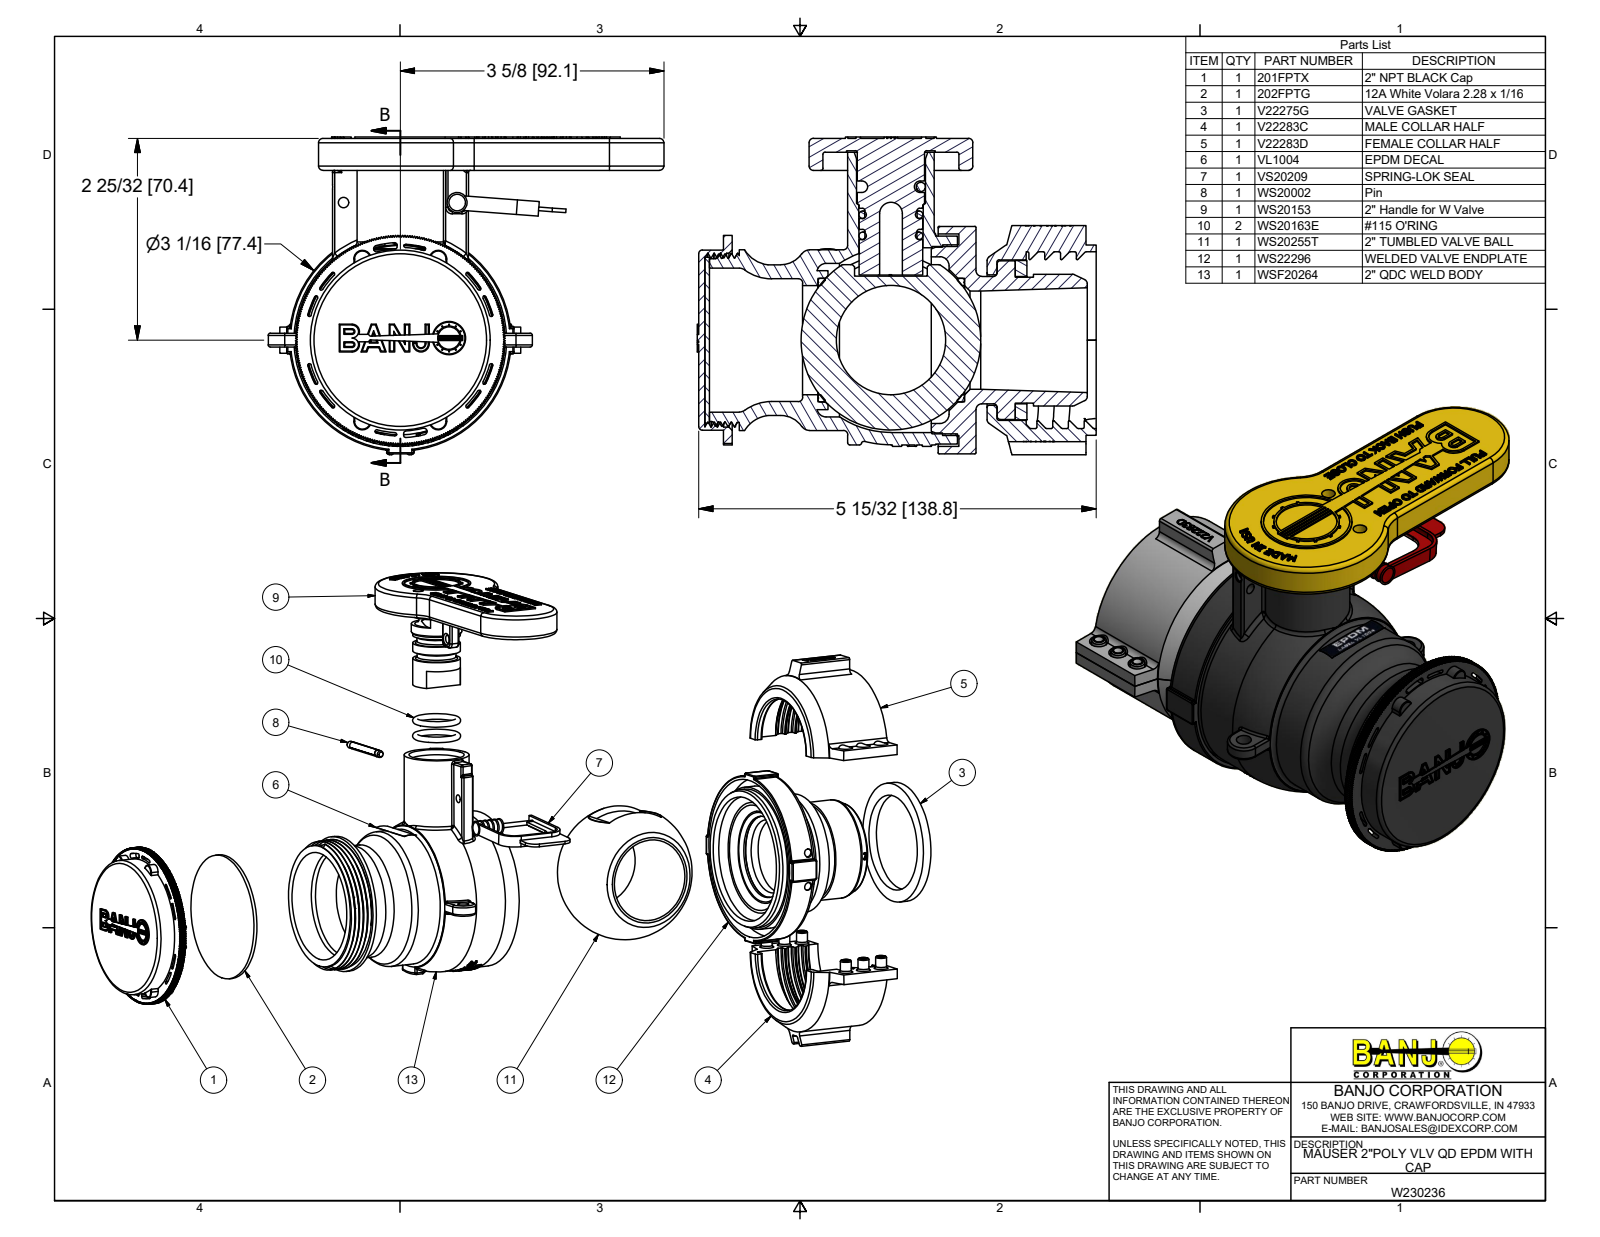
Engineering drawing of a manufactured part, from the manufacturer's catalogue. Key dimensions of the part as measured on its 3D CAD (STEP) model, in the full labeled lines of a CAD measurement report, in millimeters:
Part name (STEP PRODUCT): W230236; VS20209; 201FPTX; 202FPTG (+8 more)
STEP written by: Autodesk Inventor 2018 (AUTOMOTIVE_DESIGN)
Units: millimetres
Bodies: 16 solids, 3806 faces (1880 planar, 937 cylindrical, 989 other)
Overall size (bounding box): 139.3 × 138.2 × 110.9
Volume: 332 500 mm³ · Surface area: 164 500 mm²
Round holes (diameter × count): ⌀5.3 ×6, ⌀6.5 ×6, ⌀3.7 ×2, ⌀3.8 ×2, ⌀4.8 ×2, ⌀5.3 ×2, ⌀38.1 ×2, ⌀4 ×1, ⌀7.8 ×1, ⌀7.9 ×1, ⌀11.1 ×1, ⌀21.3 ×1
Round bosses / shafts (diameter × count): ⌀5.1 ×6, ⌀77.4 ×1, ⌀74.2 ×1, ⌀73.2 ×1, ⌀72.6 ×1, ⌀66.5 ×1, ⌀66.4 ×1, ⌀64.8 ×1
Partial cylindrical surfaces — rounded edges, fillets, slot ends (radius × count): R0.8 ×68, R0.4 ×24, R2.3 ×10, R1.5 ×4, R3 ×4, R6.4 ×4, R0.3 ×3, R1.8 ×3
Main face-to-face distances: 1.6, 2.2, 4.8, 3.8, 93.1, 94.7, 96.8, 6.4, 0.5, 13.7
Hole centre spacings: 73.2, 72.6, 9.5, 9.5, 19.1, 27.2, 41.5, 51.9
